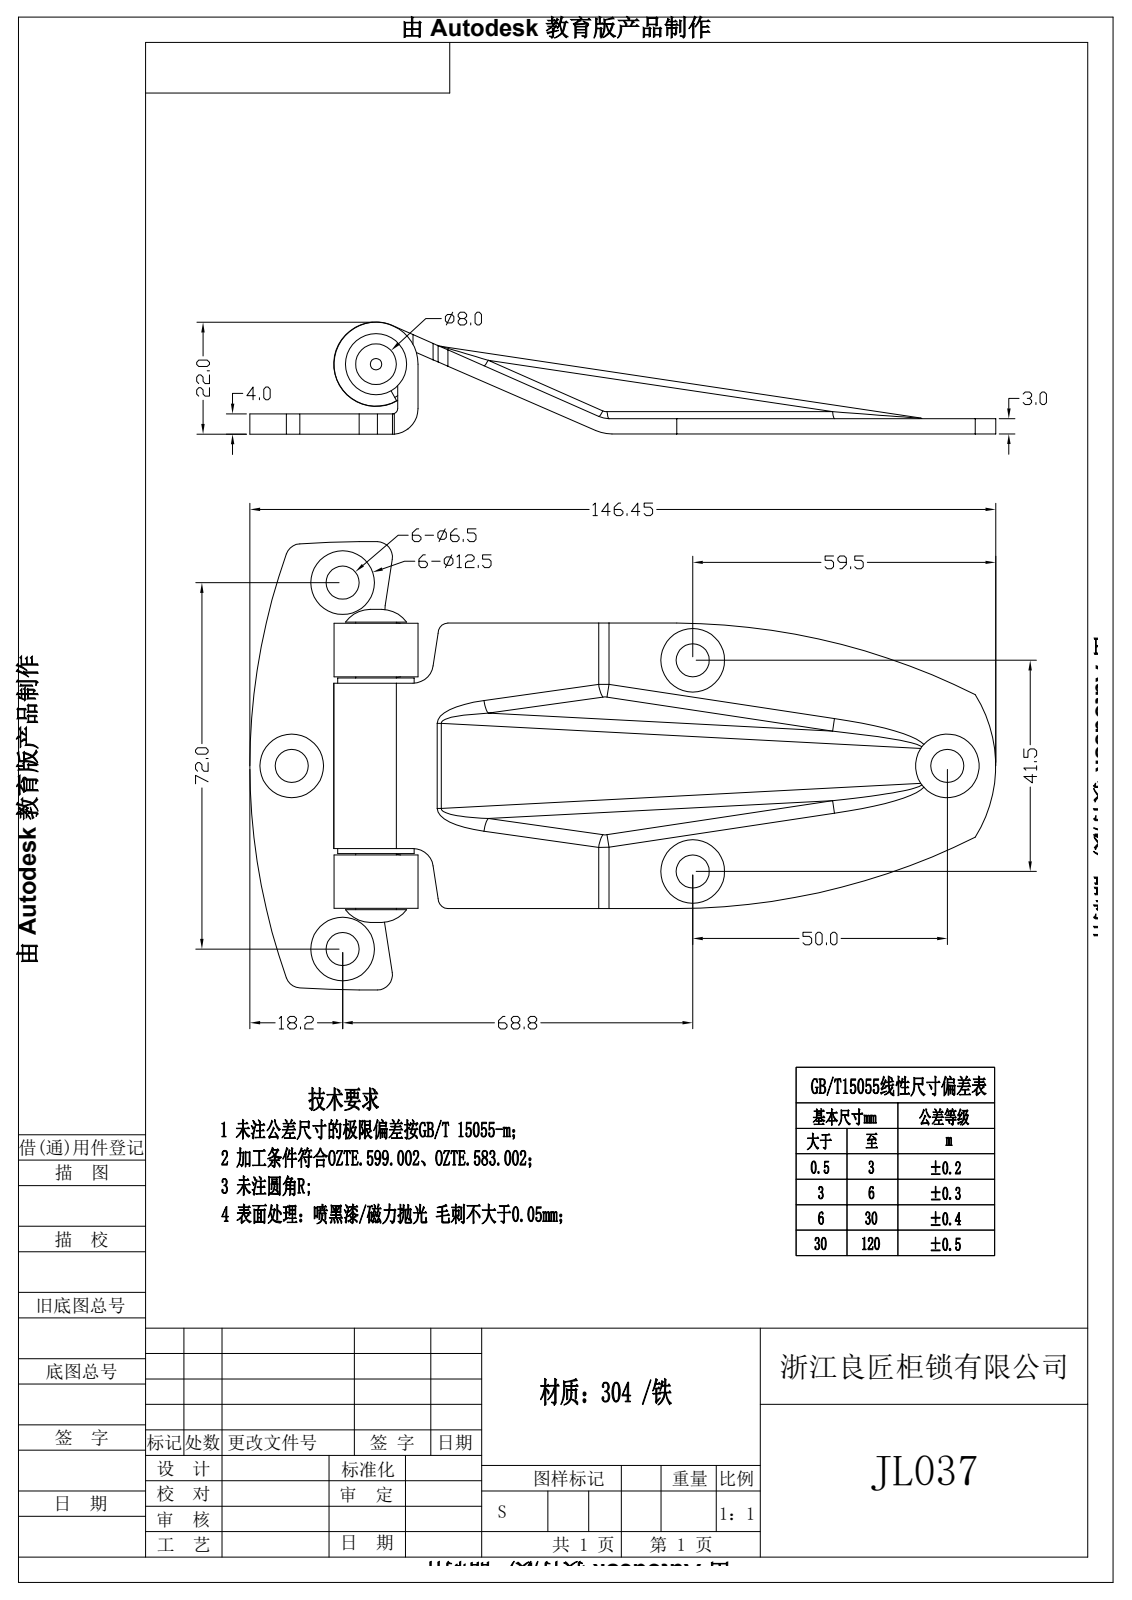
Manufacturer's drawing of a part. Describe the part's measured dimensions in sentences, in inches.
Its 3-D file was written by "Rhino 8.5 (CONFIG_CONTROL_DESIGN)". It is 2 solids with 125 faces: 59 planar, 38 cylindrical and 28 other. Overall it measures 5.766 by 3.467 by 0.868 inches. Its volume is 1.654 cubic inches and its surface area 42.31 square inches. Round holes: 1 of diameter 0.417. Round bosses or shafts: 1 of diameter 0.654, 1 of diameter 0.65, 1 of diameter 0.472, 1 of diameter 0.335. Partial cylindrical surfaces (rounded edges, fillets, slot ends): 8 of radius 0.059, 4 of radius 0.118, 3 of radius 0.315, 2 of radius 5.217, 2 of radius 8.492, 1 of radius 0.246, 1 of radius 1.043, 1 of radius 4.921. The main face-to-face distances are 0.118, 0.12, 0.157, 0.156, 0.037, 0.413, 1.795, 0.465, 1.744, 0.051.
